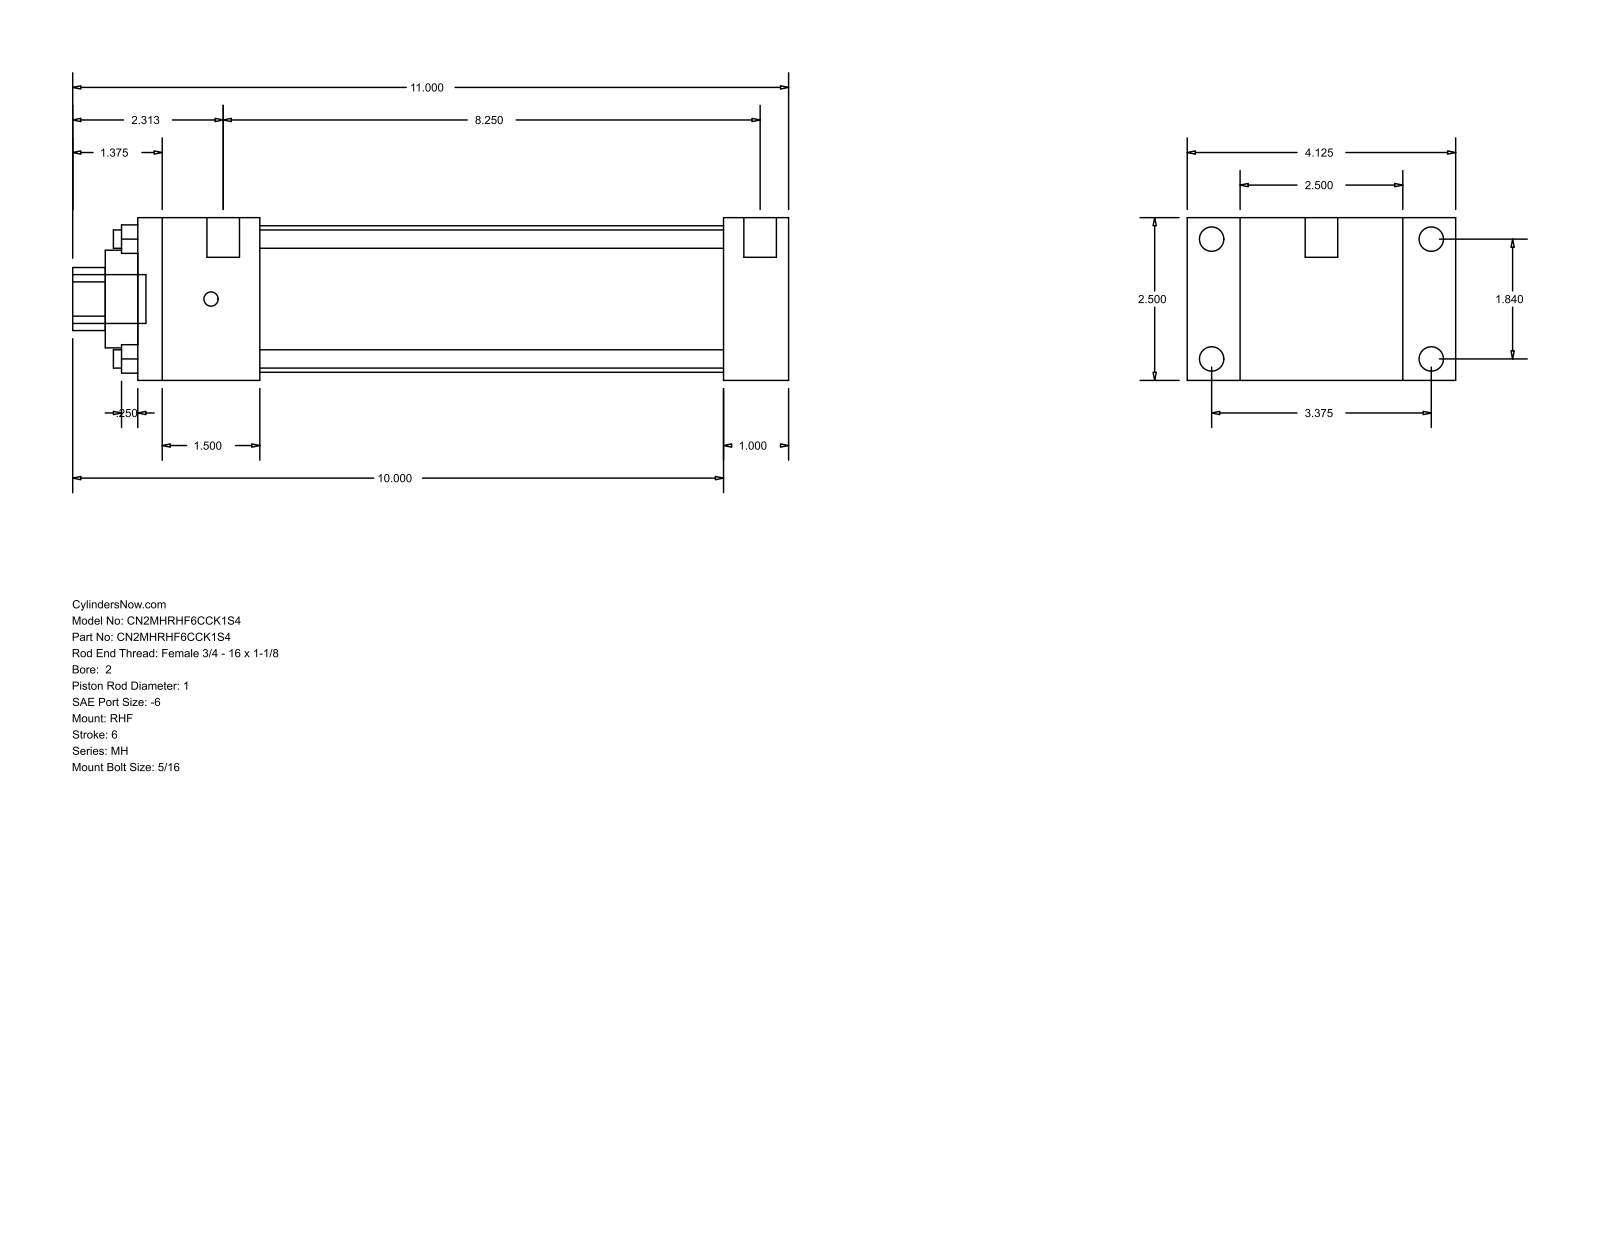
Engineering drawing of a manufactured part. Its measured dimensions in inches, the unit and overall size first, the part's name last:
Units: inches
Overall size (bounding box): 11 × 4.125 × 2.5
Round holes (diameter × count): ⌀0.281 ×4, ⌀1 ×1, ⌀1.5 ×1, ⌀2.25 ×1
Round bosses / shafts (diameter × count): ⌀0.375 ×4, ⌀0.219 ×4, ⌀0.5 ×2, ⌀0.75 ×1
Partial cylindrical surfaces — rounded edges, fillets, slot ends (radius × count): R0.484 ×1
Main face-to-face distances: 2.5, 1, 0.813, 3.313, 10, 9, 4.125, 1.875, 7.125, 8.125
Hole centre spacings: 1.301, 1.84, 2.602
Bodies: 0 solids, 88 faces (60 planar, 28 cylindrical, 0 other)
Part name (STEP PRODUCT): MH_RHF__0200_1
STEP written by: GSSL Pune (CONFIG_CONTROL_DESIGN)
